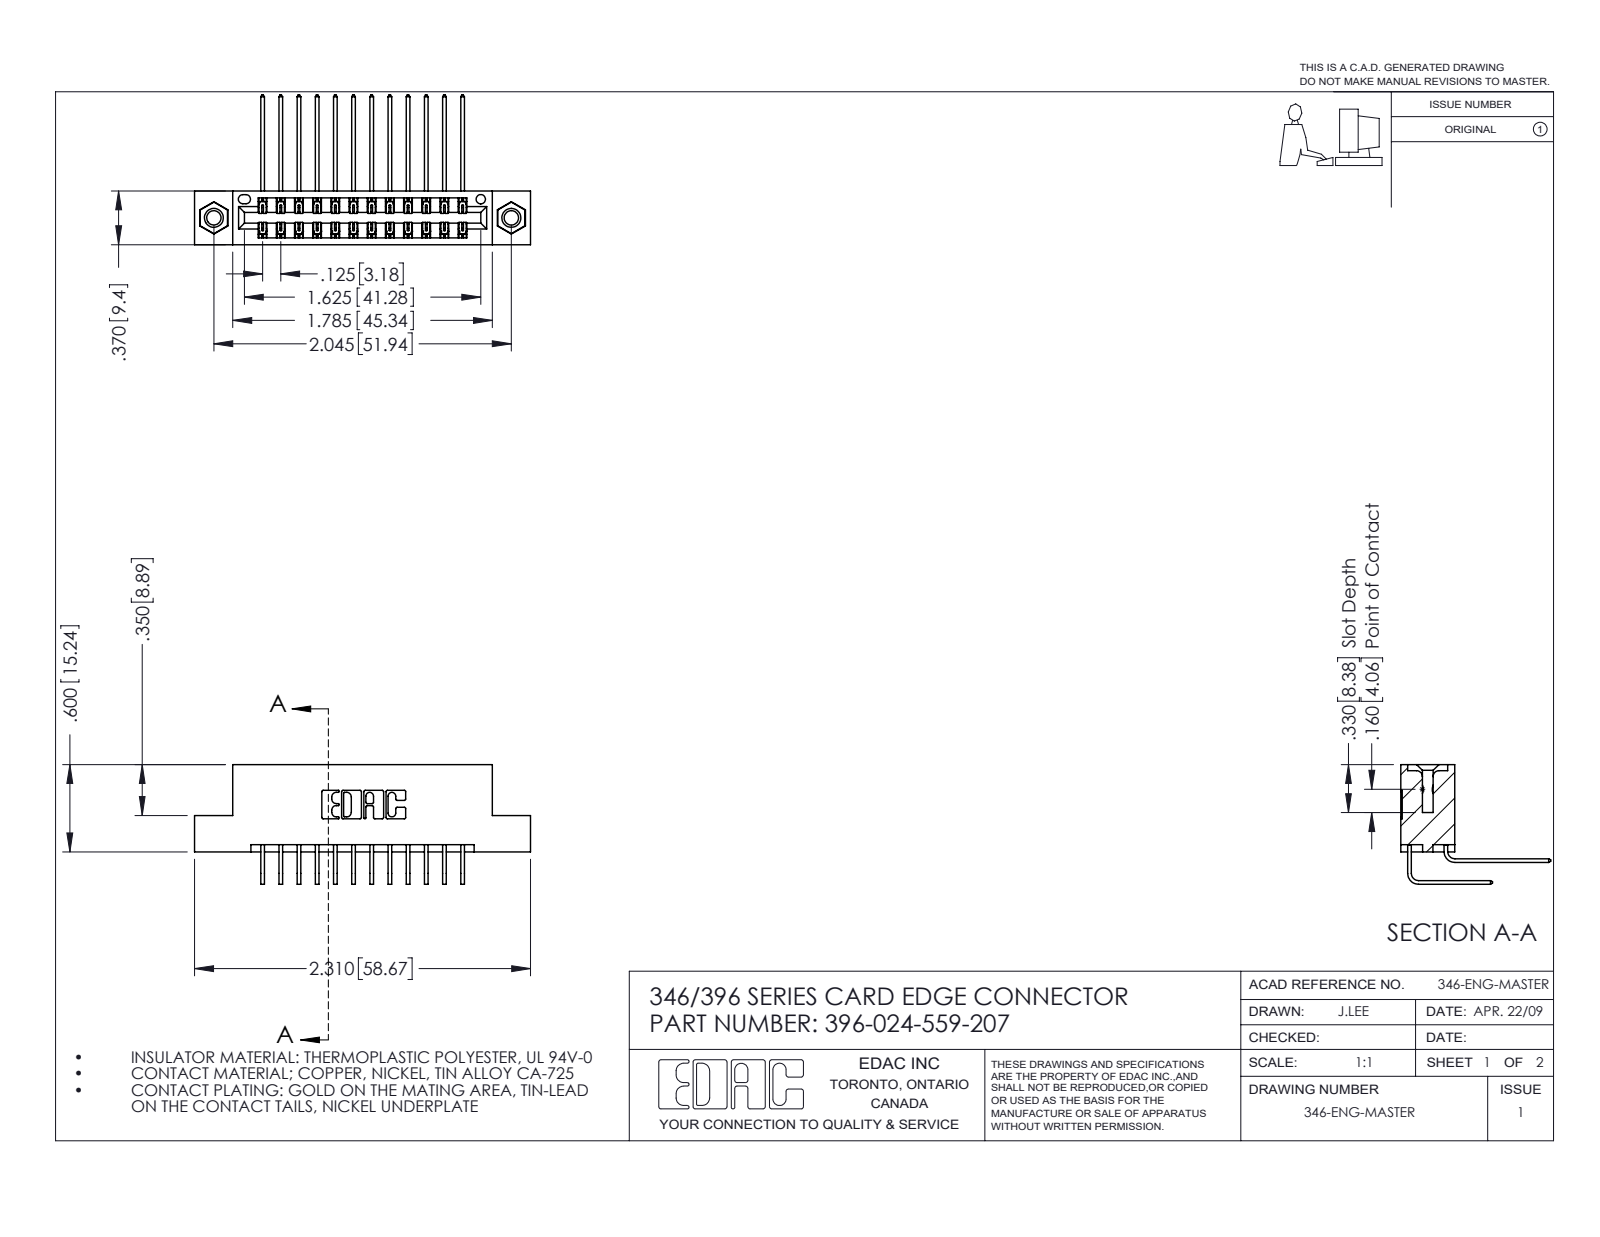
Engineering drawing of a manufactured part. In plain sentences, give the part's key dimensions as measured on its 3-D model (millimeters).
The part is named "396-024-559-207; 345-250-001_345-250-005-103; 345-292-001_559 Tail - 2; 345-292-001_558 559 Tail - 1 (+1 more)". Its 3-D file was written by "SolidWorks 2016 (CONFIG_CONTROL_DESIGN)". It is 27 solids with 1478 faces: 996 planar, 466 cylindrical and 16 other. Overall it measures 58.7 by 26.2 by 20.9 millimeters. Its volume is 5 620 cubic millimeters and its surface area 7 942 square millimeters. Round holes: 2 of diameter 2.5, 2 of diameter 3.2, 2 of diameter 4, 1 of diameter 1.6. Round bosses or shafts: 2 of diameter 3.9. Partial cylindrical surfaces (rounded edges, fillets, slot ends): 36 of radius 0.2, 22 of radius 0.3, 6 of radius 0.2, 6 of radius 0.8, 3 of radius 0.7, 2 of radius 0.4, 2 of radius 0.6, 2 of radius 0.6. The main face-to-face distances are 1.2, 8.2, 6.4, 9.4, 0.6, 1.8, 7.6, 7, 3.8, 5.6. The hole center spacings are 6.2, 46.7, 51.9.
